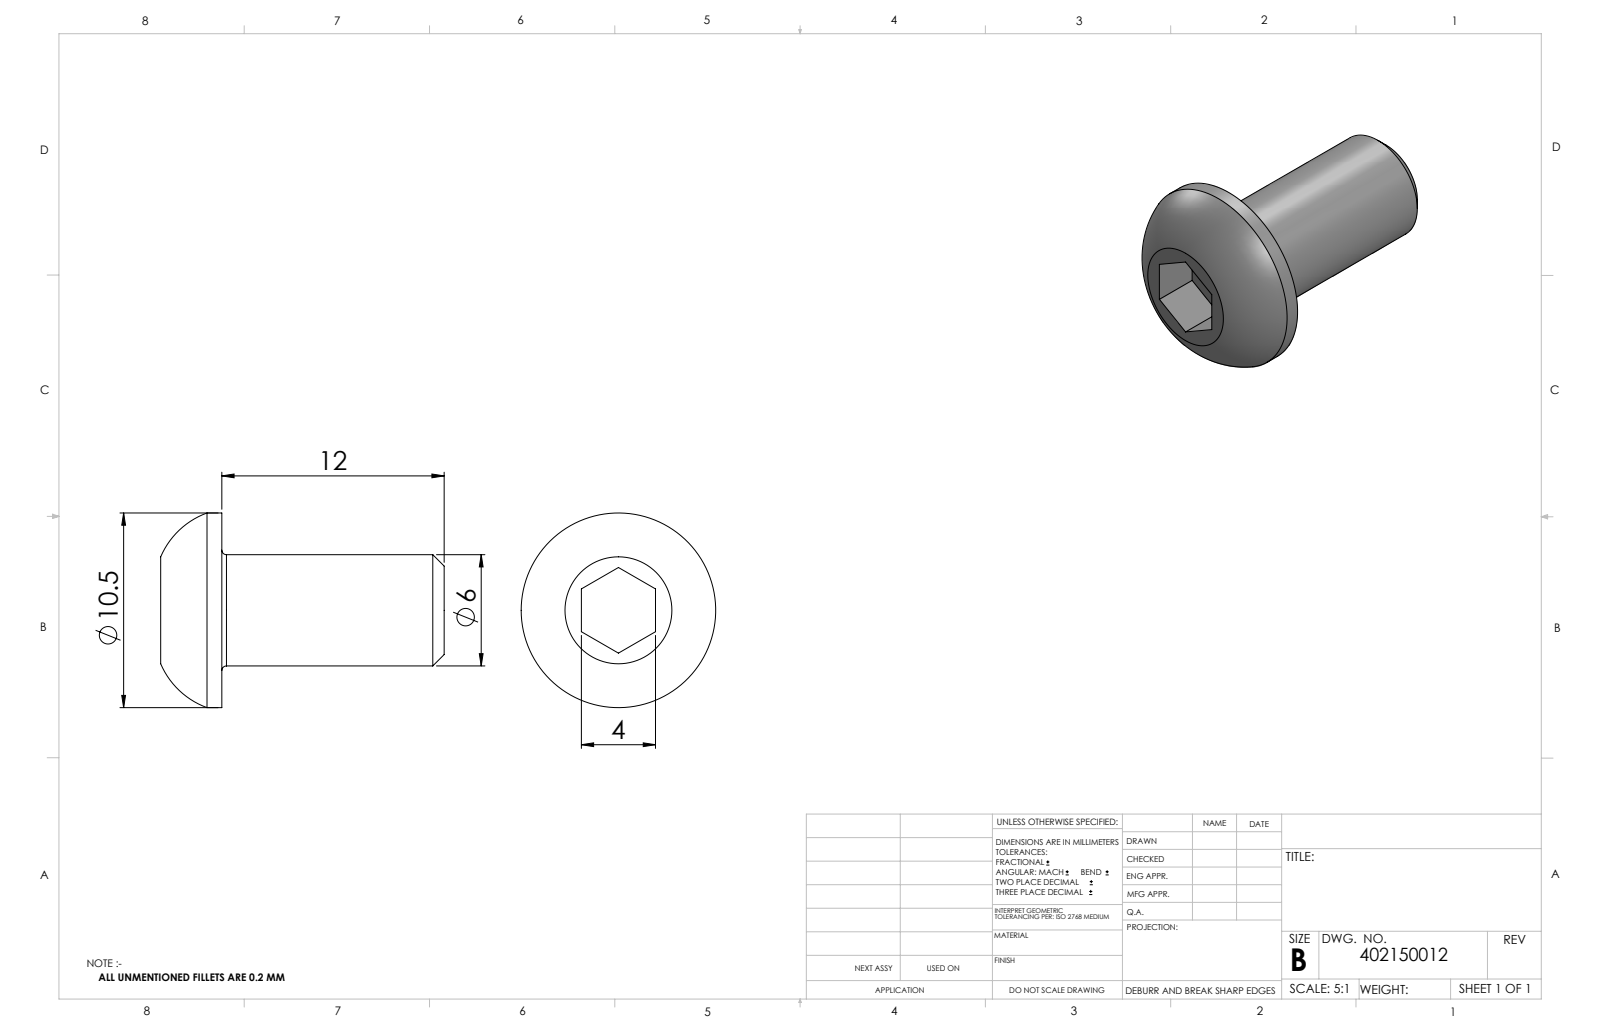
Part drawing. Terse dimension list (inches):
name: 402150012_c_1
written by: SolidWorks 2014 (CONFIG_CONTROL_DESIGN)
unit: in
bodies: 1 solid, 20 faces (10 planar, 4 cylindrical, 6 other)
size: 0.602 × 0.413 × 0.413
volume: 0.032 in³; area: 0.752 in²
bosses: 1× ⌀0.413, 1× ⌀0.236
face distances: 0.472, 0.157, 0.504, 0.031, 0.602, 0.13, 0.098
